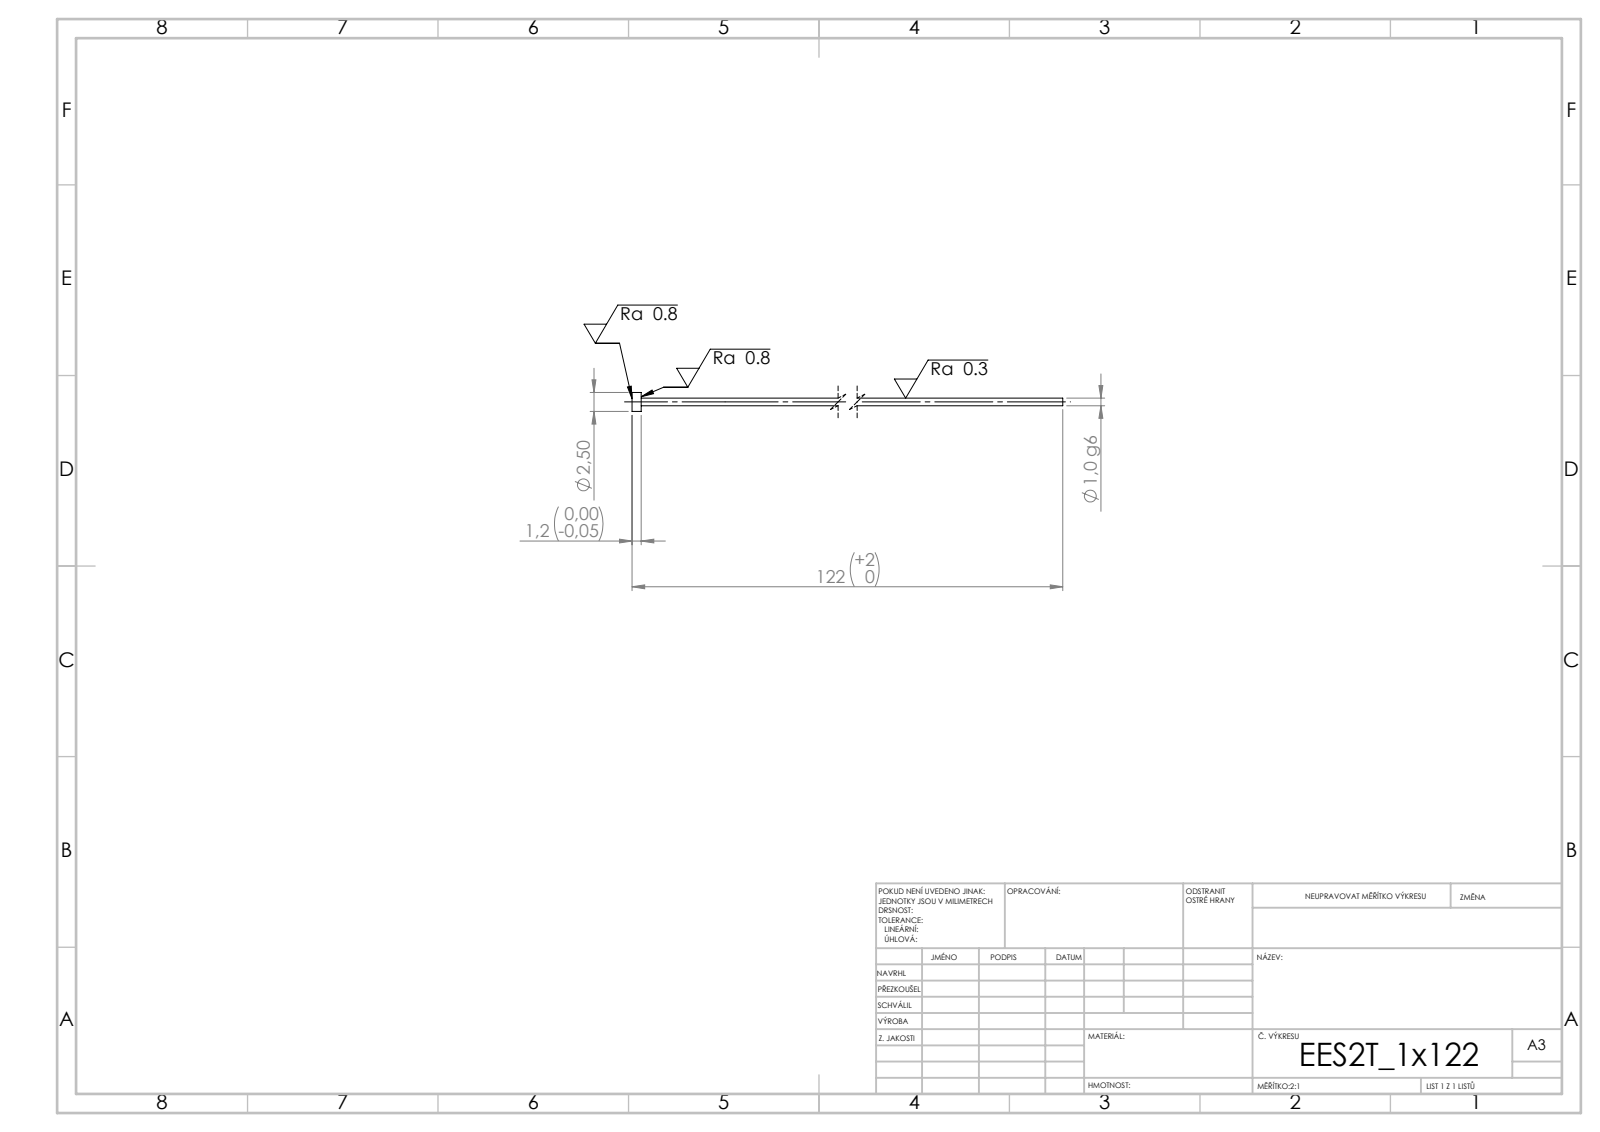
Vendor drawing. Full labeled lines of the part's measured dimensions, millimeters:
STEP written by: SolidWorks 2019 (CONFIG_CONTROL_DESIGN)
Units: millimetres
Bodies: 1 solid, 7 faces (3 planar, 4 cylindrical, 0 other)
Overall size (bounding box): 122 × 2.5 × 2.5
Volume: 101 mm³ · Surface area: 399 mm²
Round bosses / shafts (diameter × count): ⌀2.5 ×1, ⌀1 ×1
Main face-to-face distances: 1.2, 122, 120.8
